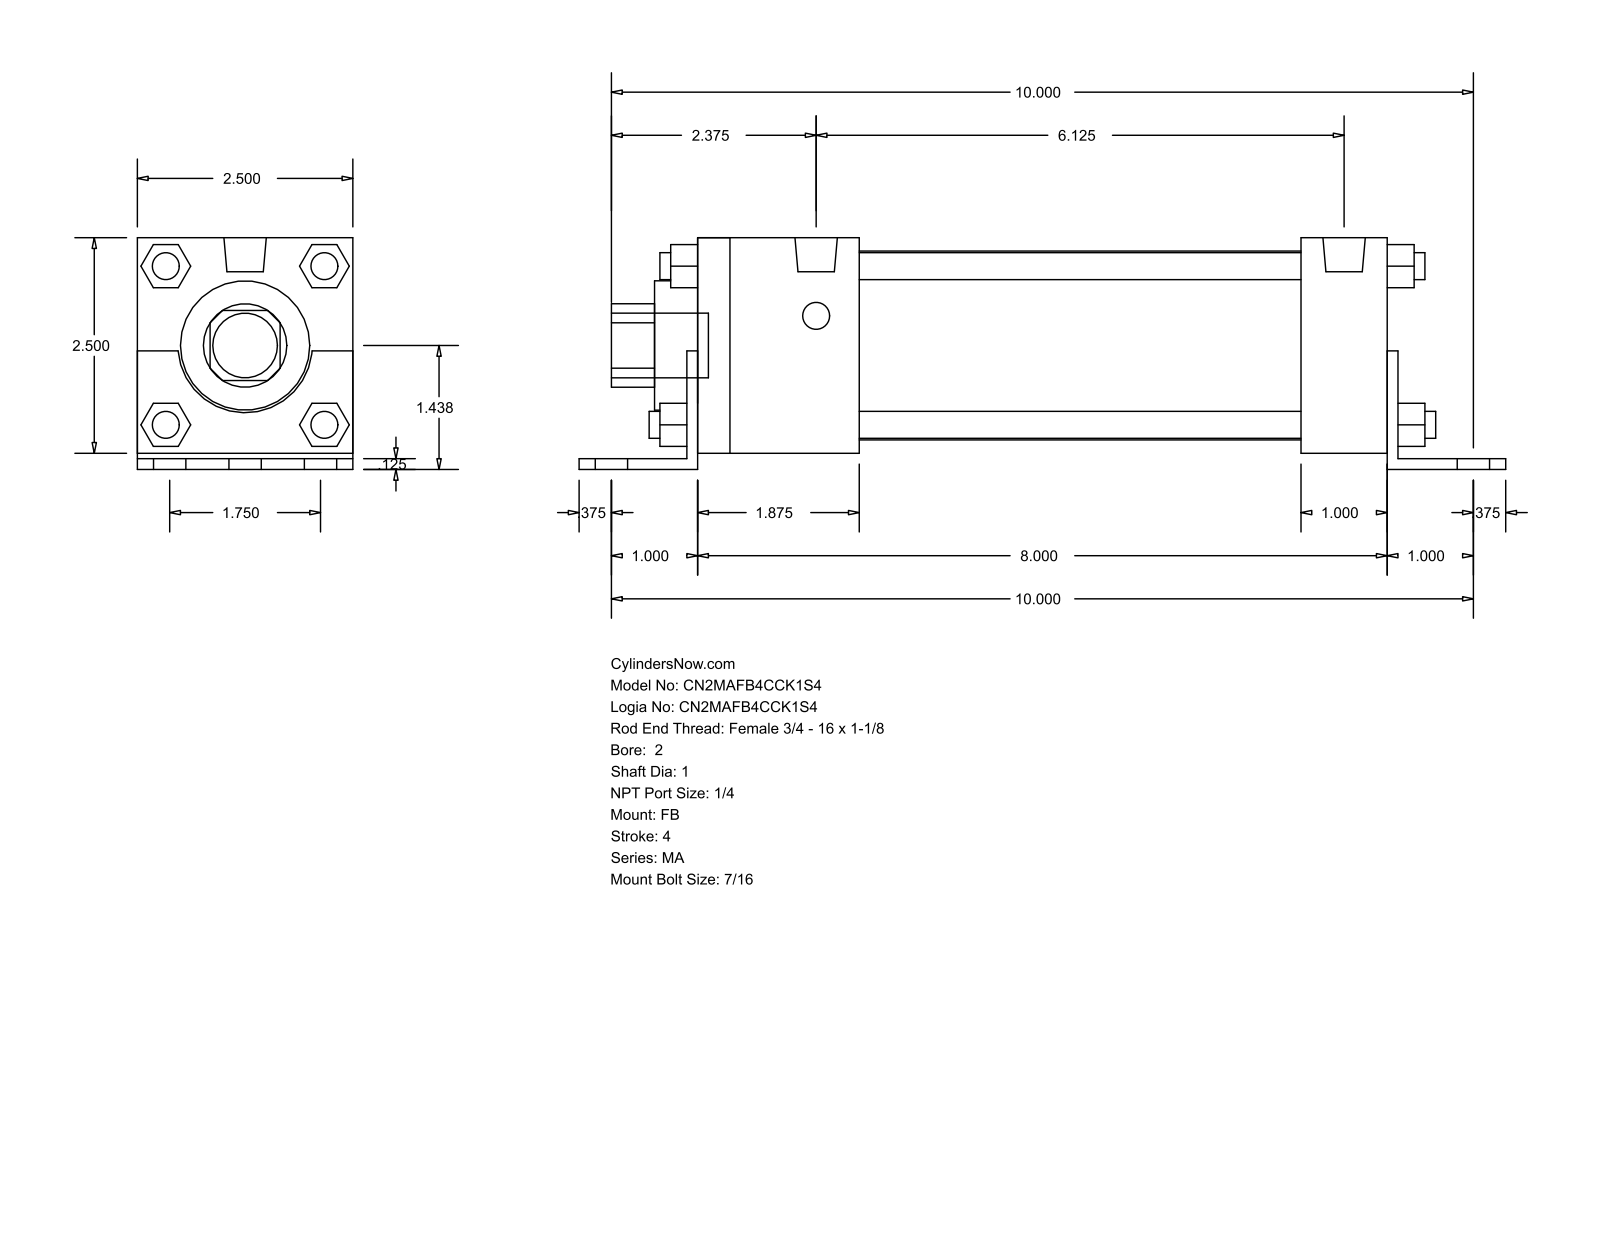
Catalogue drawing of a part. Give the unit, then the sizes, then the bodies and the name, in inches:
Units: inches
Overall size (bounding box): 10.75 × 2.687 × 2.5
Round holes (diameter × count): ⌀1 ×1, ⌀1.5 ×1, ⌀2.19 ×1
Round bosses / shafts (diameter × count): ⌀0.313 ×8, ⌀0.437 ×6, ⌀0.492 ×2, ⌀0.75 ×1
Partial cylindrical surfaces — rounded edges, fillets, slot ends (radius × count): R0.484 ×1, R0.78 ×1
Main face-to-face distances: 2.5, 0.125, 0.187, 2.687, 0.063, 2.563, 0.5, 0.125, 8, 8.125
Bodies: 0 solids, 140 faces (105 planar, 35 cylindrical, 0 other)
Part name (STEP PRODUCT): MA_FB__0200_1
STEP written by: GSSL Pune (CONFIG_CONTROL_DESIGN)
